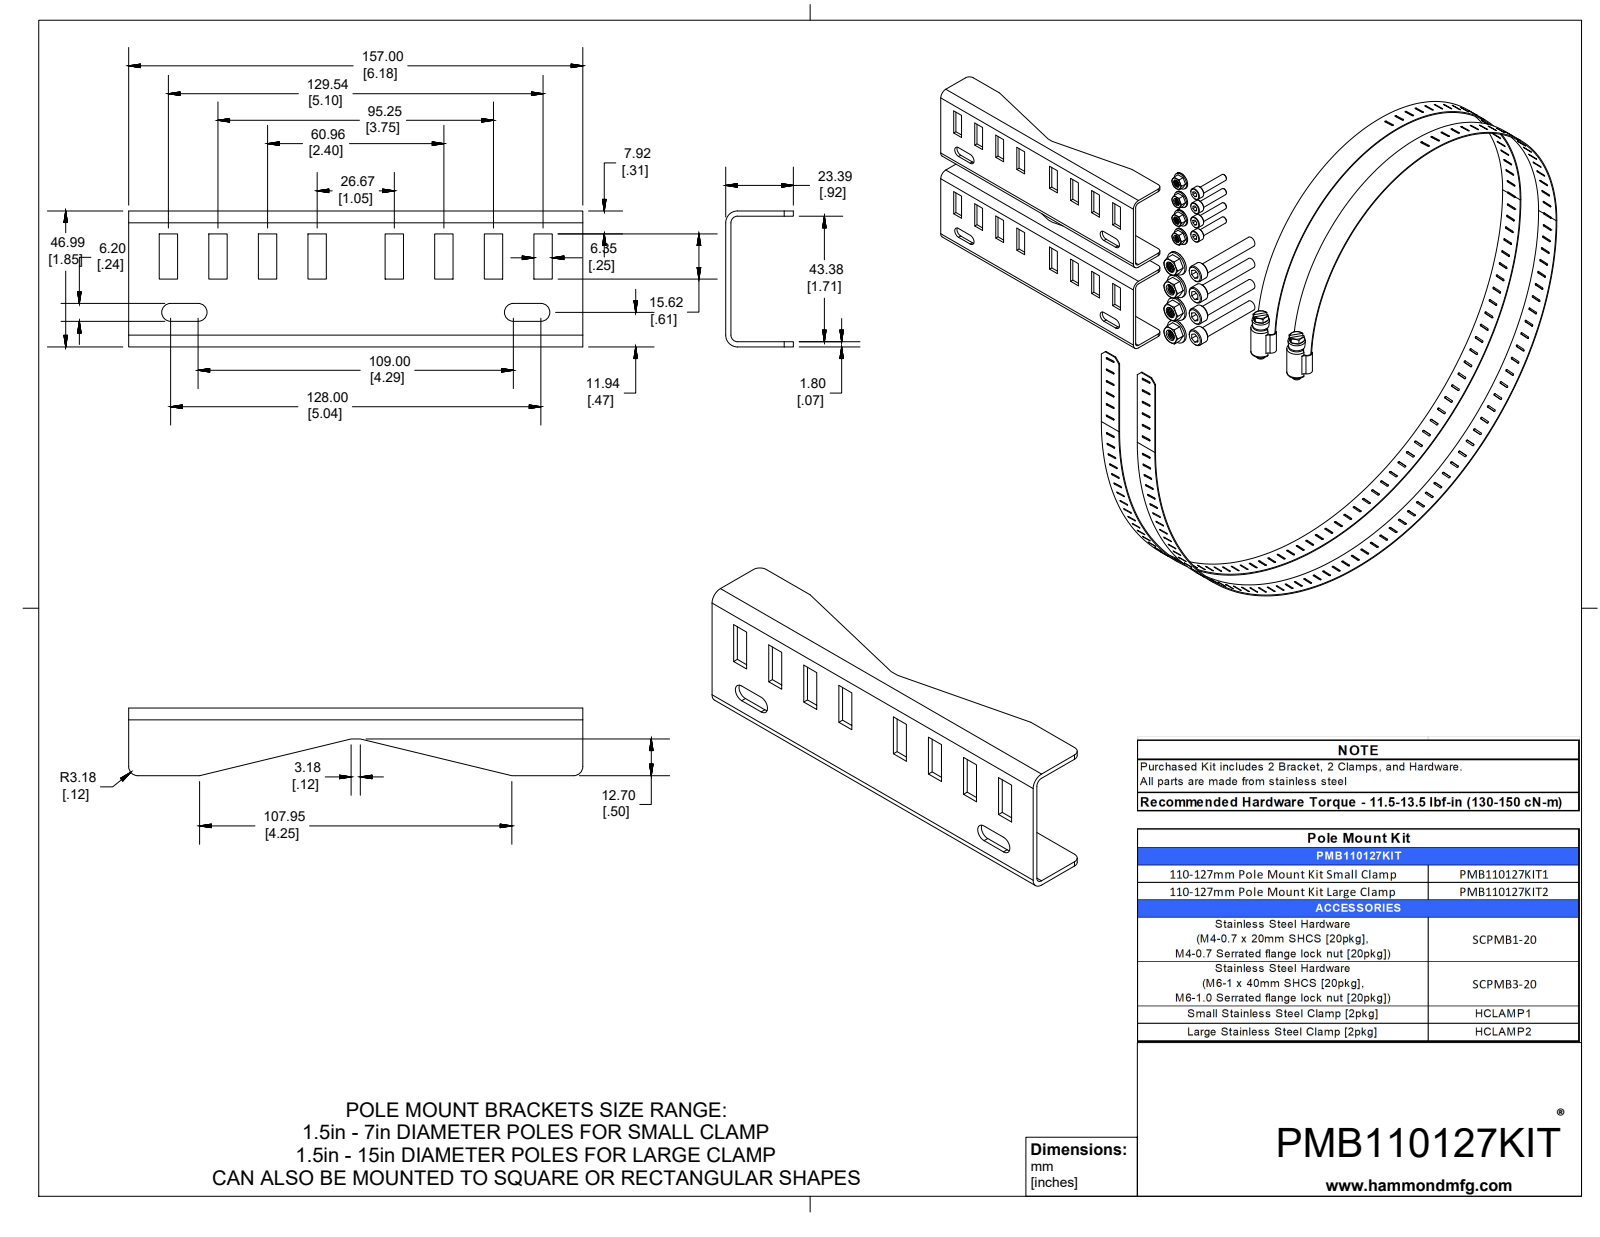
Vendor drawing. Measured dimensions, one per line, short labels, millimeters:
name: PMB110127KIT1
written by: SolidWorks 2019 (CONFIG_CONTROL_DESIGN)
unit: mm
bodies: 22 solids, 1814 faces (1220 planar, 472 cylindrical, 122 other)
size: 327.6 × 299.8 × 264.1
volume: 68 060 mm³; area: 115 400 mm²
holes: 4× ⌀3.3, 4× ⌀4.2, 4× ⌀4.7, 4× ⌀6
bosses: 8× ⌀10, 4× ⌀14.2, 4× ⌀10.6, 4× ⌀7.4, 4× ⌀6.9, 4× ⌀6, 4× ⌀4, 2× ⌀8
rounds: 364× R0.5, 9× R3.2, 8× R3.1, 4× R2.3, 4× R2.5, 4× R3, 4× R4.1, 2× R5
face distances: 1.8, 57, 45.2, 58.8, 102.2, 43.4, 10, 1.8, 13.6, 47
hole spacings: 13, 16, 26.1, 32, 13.1, 16, 22.9, 35.7
